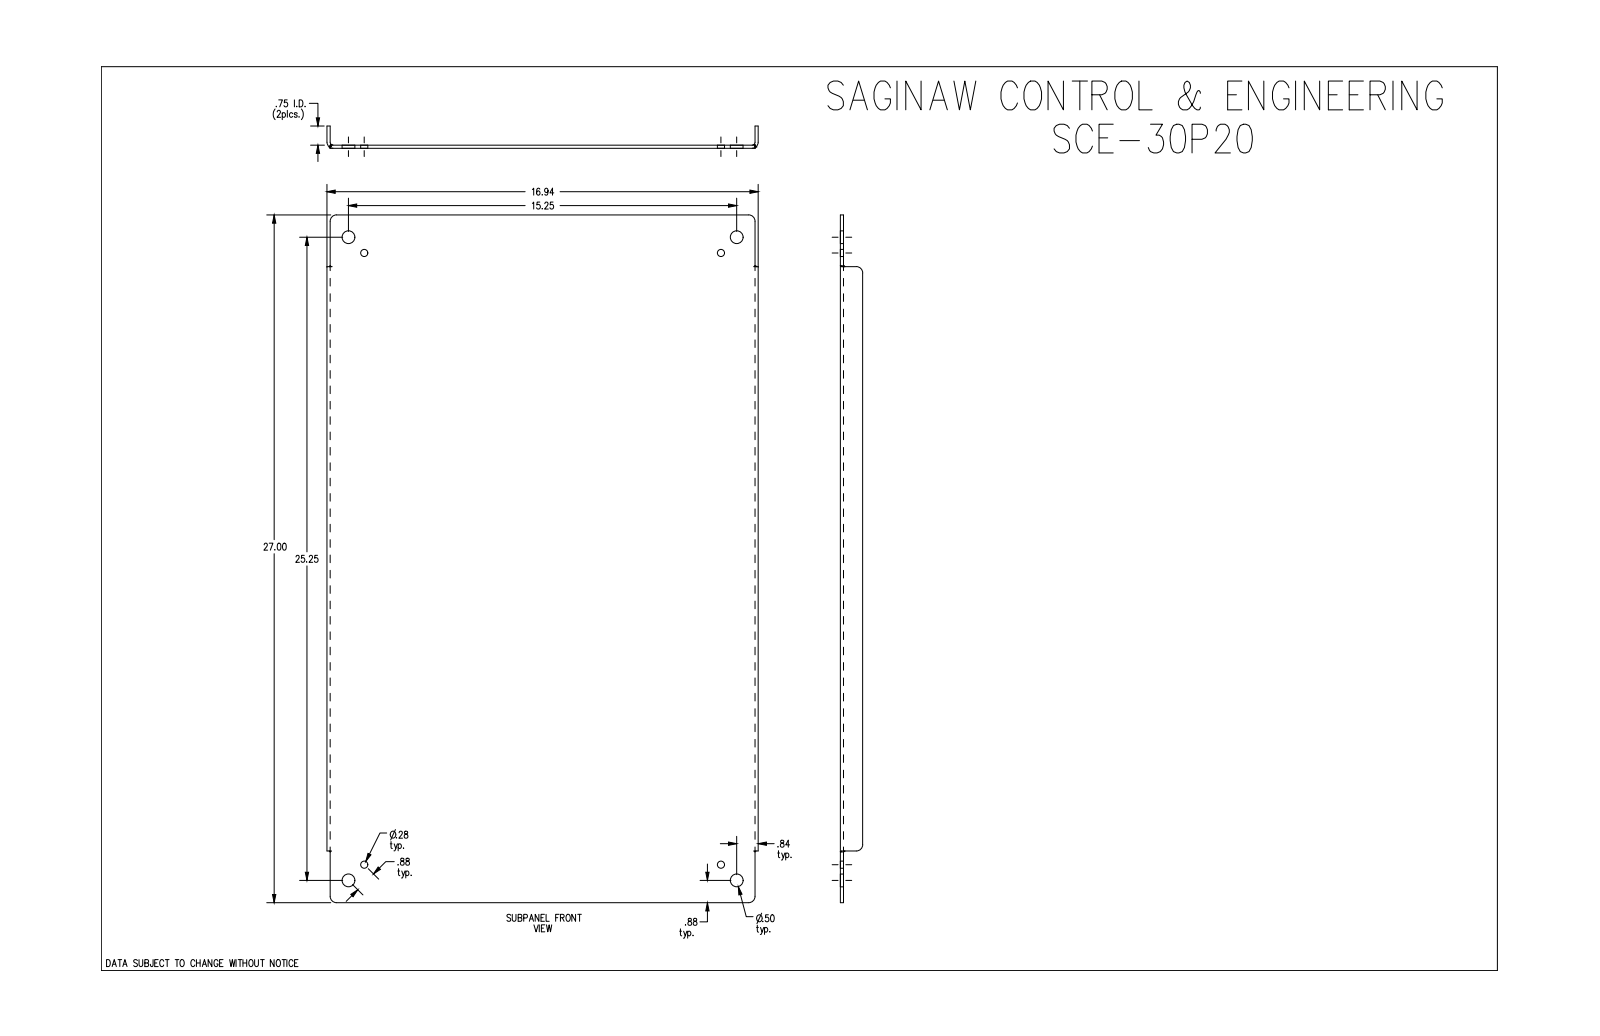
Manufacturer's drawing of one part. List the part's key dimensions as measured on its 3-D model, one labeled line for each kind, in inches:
Part name (STEP PRODUCT): SCE-30P20
STEP written by: SolidWorks 2019 (CONFIG_CONTROL_DESIGN)
Units: inches
Bodies: 1 solid, 50 faces (18 planar, 20 cylindrical, 12 other)
Overall size (bounding box): 27 × 16.938 × 0.875
Volume: 60.77 in³ · Surface area: 984.7 in²
Round holes (diameter × count): ⌀0.281 ×4, ⌀0.5 ×4
Partial cylindrical surfaces — rounded edges, fillets, slot ends (radius × count): R0.25 ×6, R0.112 ×2, R0.237 ×2
Main face-to-face distances: 0.125, 0.125, 16.813, 16.687, 16.938, 0.75, 0.875, 27, 2.031, 24.969
Hole centre spacings: 0.875, 14.644, 24.639, 28.649, 14.013, 15.25, 24.013, 25.25
